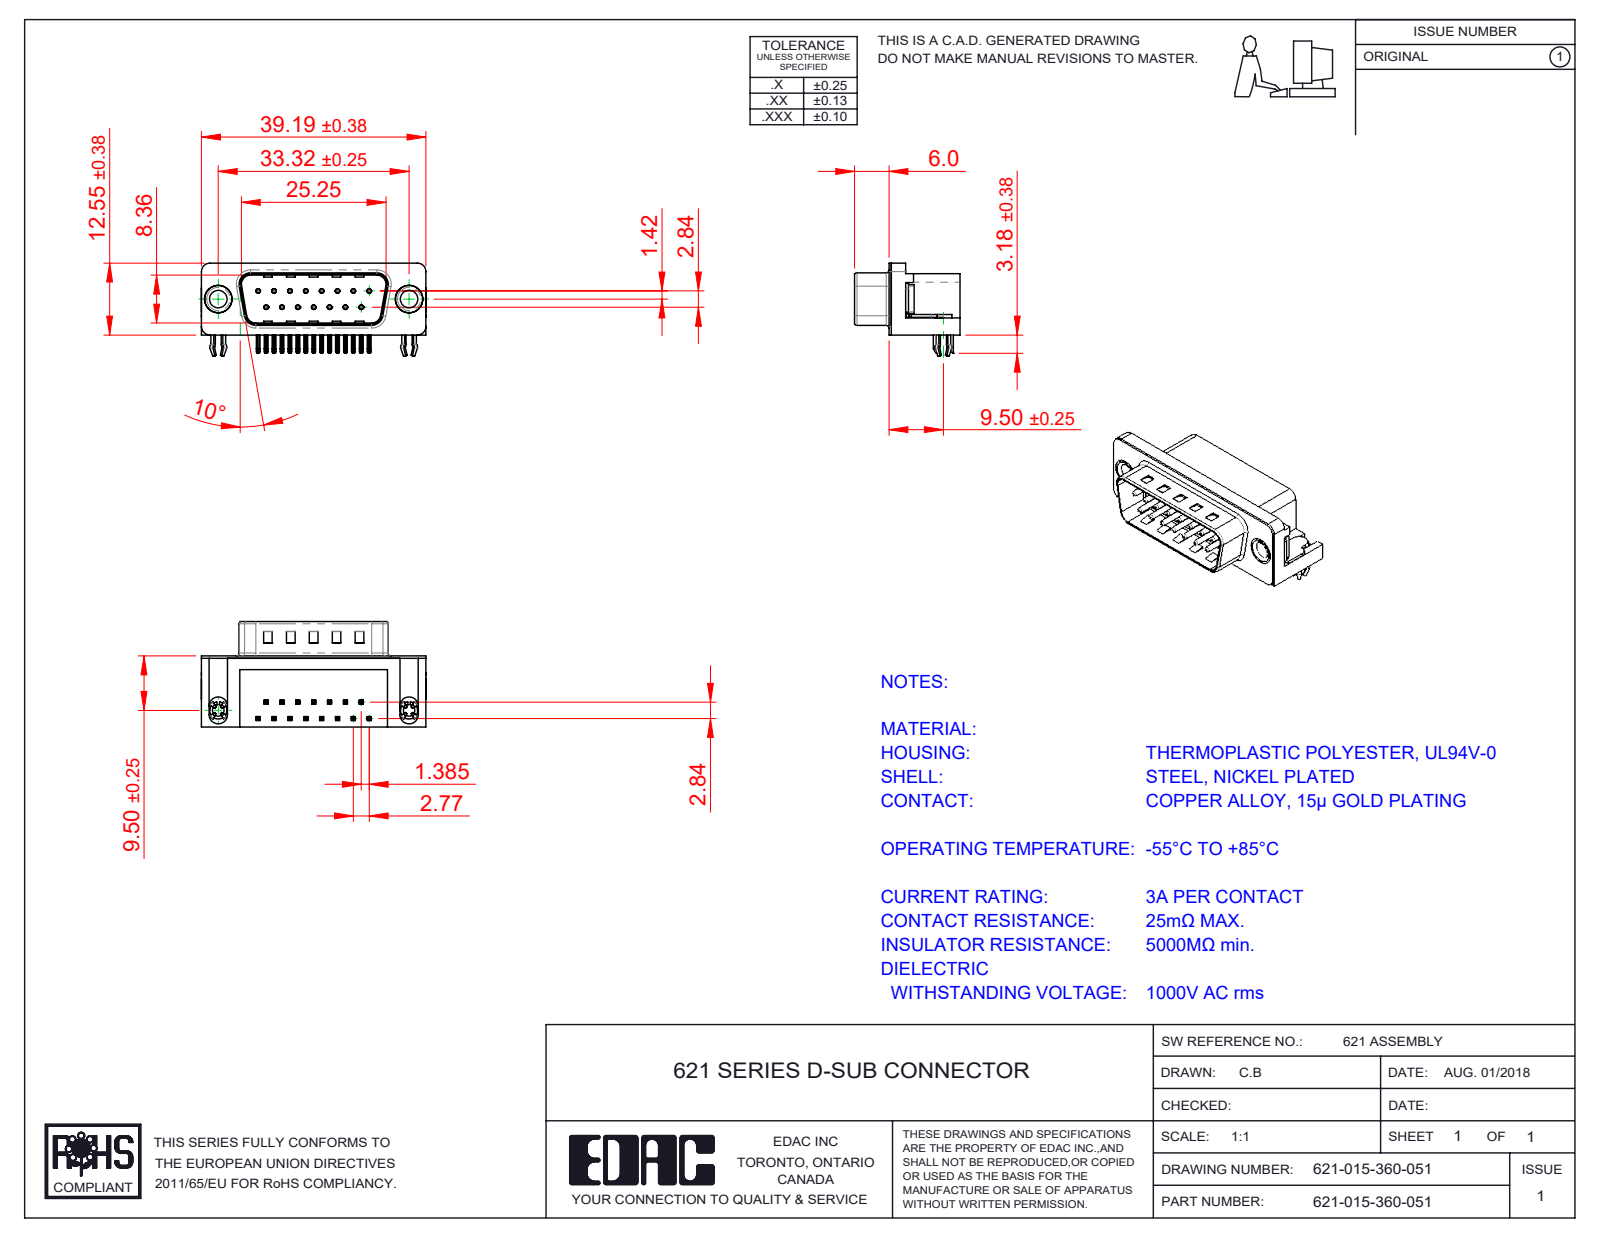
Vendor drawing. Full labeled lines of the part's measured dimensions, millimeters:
Part name (STEP PRODUCT): 621 Housing_15 Socket; 621 Thru Hole Rivet; 621 4-40 Threaded Board Mount; 621-015-360-051 (+3 more)
STEP written by: SolidWorks 2016 (CONFIG_CONTROL_DESIGN)
Units: millimetres
Bodies: 21 solids, 1467 faces (893 planar, 439 cylindrical, 135 other)
Overall size (bounding box): 39.22 × 18.4 × 15.73
Volume: 4 414 mm³ · Surface area: 5 706 mm²
Round holes (diameter × count): ⌀0.35 ×15, ⌀0.8 ×15, ⌀2.26 ×2, ⌀3.05 ×2, ⌀4 ×2, ⌀4.8 ×2, ⌀5 ×2
Round bosses / shafts (diameter × count): ⌀0.75 ×15, ⌀4.9 ×2, ⌀4.75 ×2, ⌀3.85 ×2, ⌀3.26 ×2
Partial cylindrical surfaces — rounded edges, fillets, slot ends (radius × count): R0.25 ×68, R0.12 ×30, R1 ×16, R0.5 ×9, R1.6 ×8, R1.5 ×6, R0.9 ×4, R2 ×4
Main face-to-face distances: 0.4, 12, 10.35, 2.1, 12.4, 10.46, 1.7, 10.86, 8.76, 2.9
Hole centre spacings: 3.16, 2.77, 5.54, 8.31, 11.08, 5.03, 5.04, 7.48
